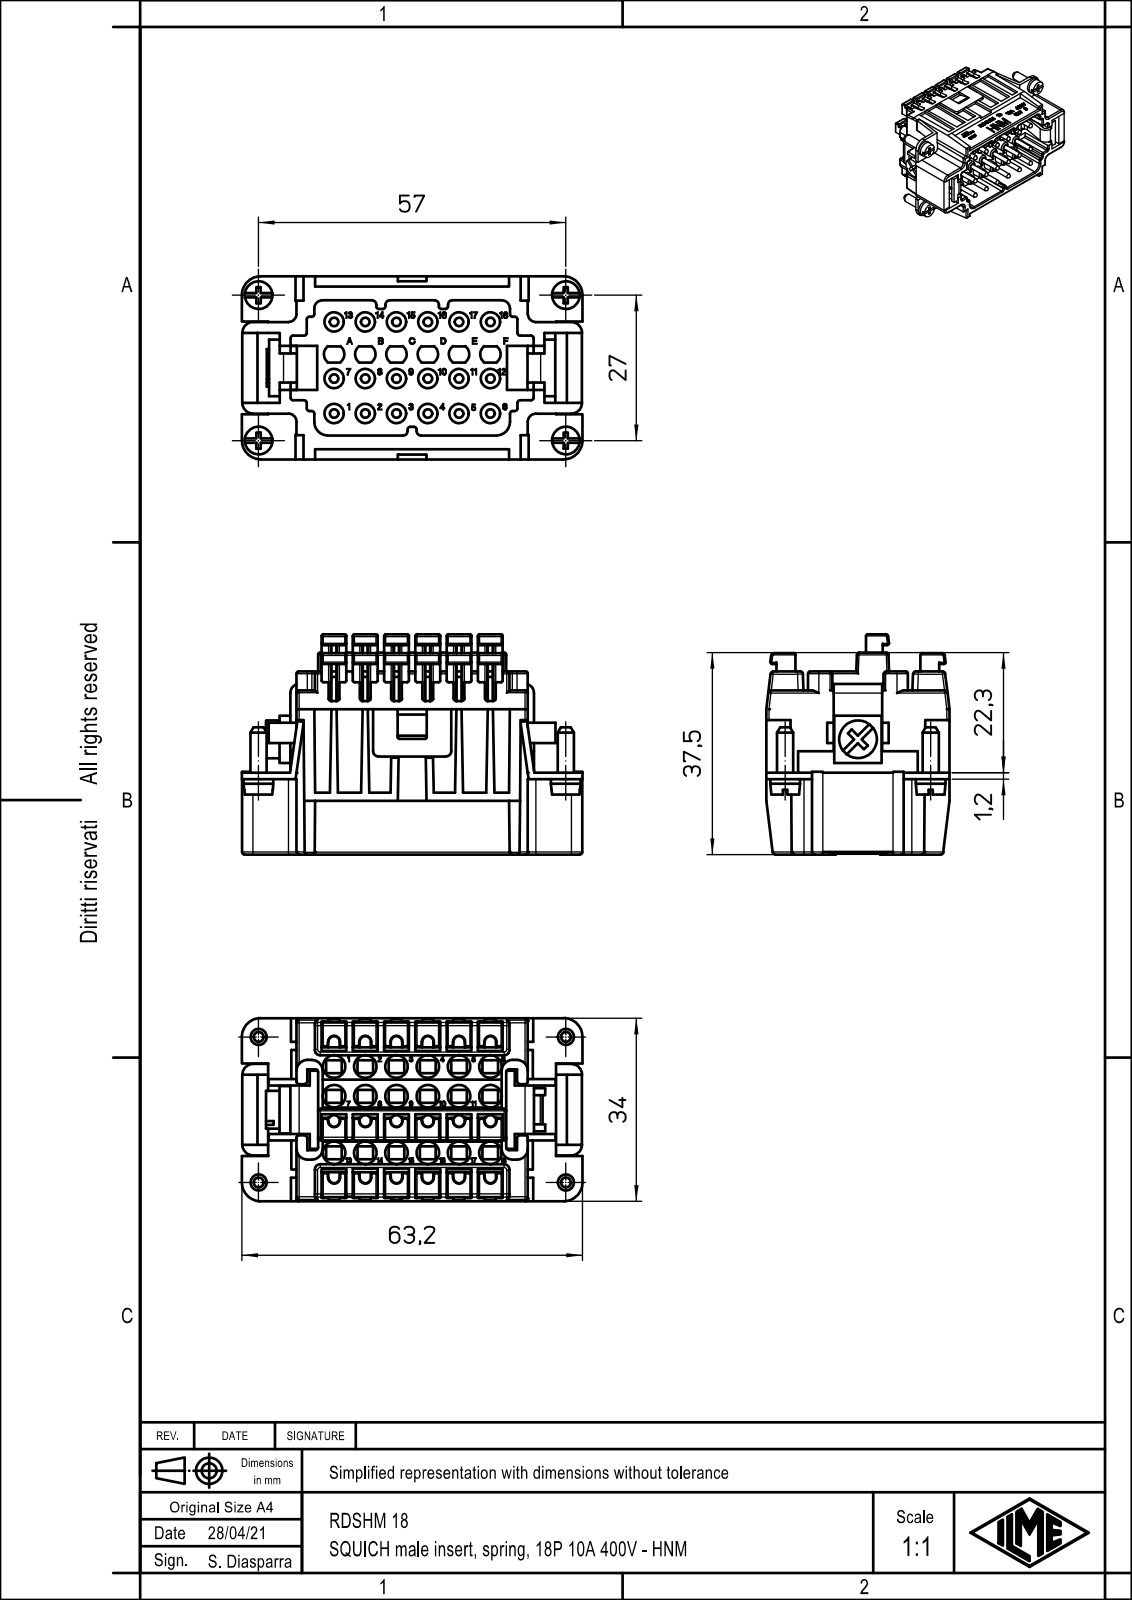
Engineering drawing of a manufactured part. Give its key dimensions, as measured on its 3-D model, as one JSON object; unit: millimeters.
{"part_name": "RDSHM_18", "step_written_by": "Creo Elements/Direct Modeling 20.1B 02-Apr-2019 (C) Parametric Technology GmbH (AUTOMOTIVE_DESIGN)", "units": "millimeters", "bodies": {"solids": 1, "faces": 2308, "planar": 1242, "cylindrical": 667, "other": 399}, "overall_size": [63.2, 40.9, 34], "volume_mm3": 37614, "surface_area_mm2": 20510, "round_holes": [[4.2, 18], [3.3, 1]], "round_bosses_or_shafts": [[1.6, 18], [5.5, 4], [3, 4], [7, 1]], "partial_cylinders_radius": [[0.3, 156], [0.5, 100], [0.2, 24], [0.4, 22], [1.05, 18], [2, 14], [0.8, 6], [1, 6]], "face_to_face_distances": [2, 1.2, 0.9, 33.1, 5.8, 25.5, 12, 34, 10.1, 18.5], "hole_center_spacings": [5.8, 11.6, 7.99, 12, 17.02, 17.4, 12.84, 15.65]}
